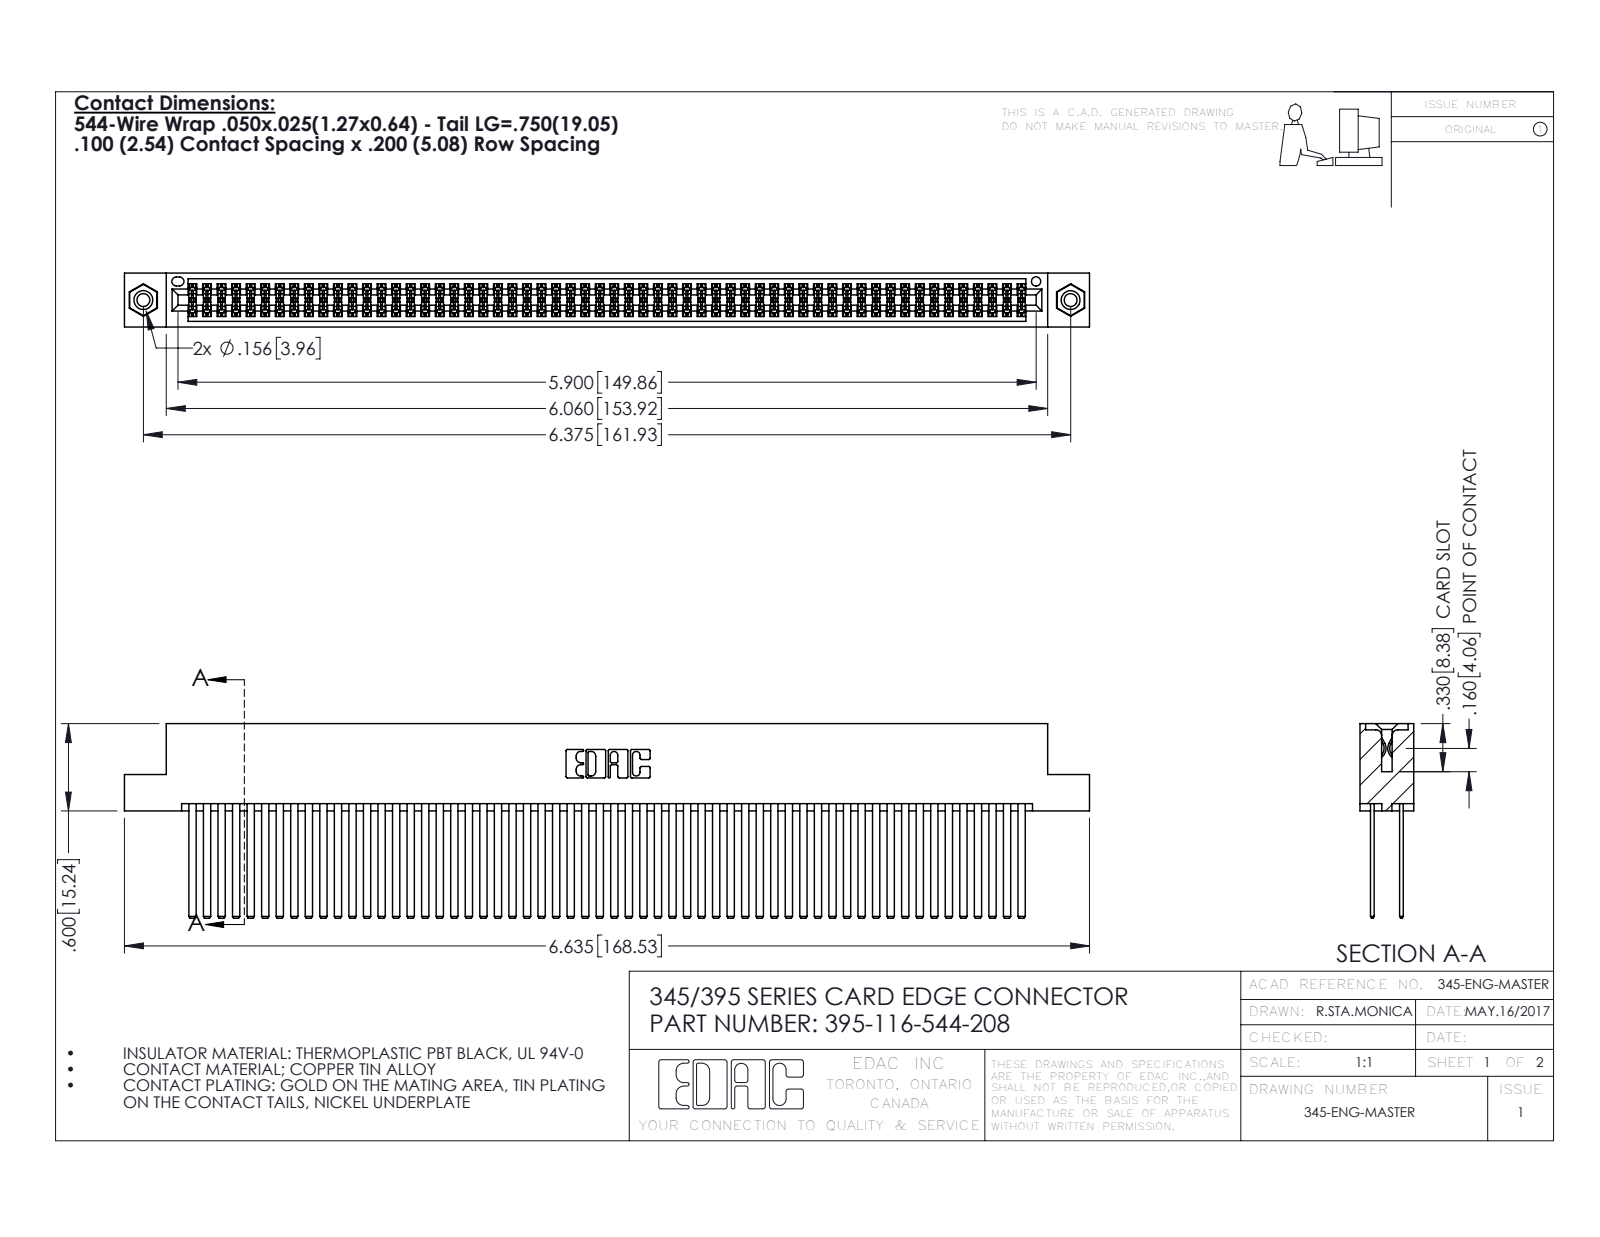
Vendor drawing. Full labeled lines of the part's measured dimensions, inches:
Part name (STEP PRODUCT): 345-292-001_345-293-144; 345 Part_Flush Mounting Lugs - 0.156 Dia-TI; 395-116-544-208; 345-250-001_345-250-003-102
STEP written by: SolidWorks 2016 (CONFIG_CONTROL_DESIGN)
Units: inches
Bodies: 119 solids, 5290 faces (3476 planar, 1798 cylindrical, 16 other)
Overall size (bounding box): 6.635 × 1.337 × 0.37
Volume: 1.107 in³ · Surface area: 49.45 in²
Round holes (diameter × count): ⌀0.089 ×2, ⌀0.125 ×2, ⌀0.156 ×2, ⌀0.064 ×1
Round bosses / shafts (diameter × count): ⌀0.155 ×2
Partial cylindrical surfaces — rounded edges, fillets, slot ends (radius × count): R0.006 ×174, R0.01 ×22, R0.007 ×6, R0.031 ×6, R0.026 ×3, R0.014 ×2, R0.019 ×2, R0.022 ×2
Main face-to-face distances: 0.2, 0.025, 0.072, 0.098, 0.272, 0.298, 0.225, 0.175, 0.37, 0.05
Hole centre spacings: 0.27, 6.139, 6.375
